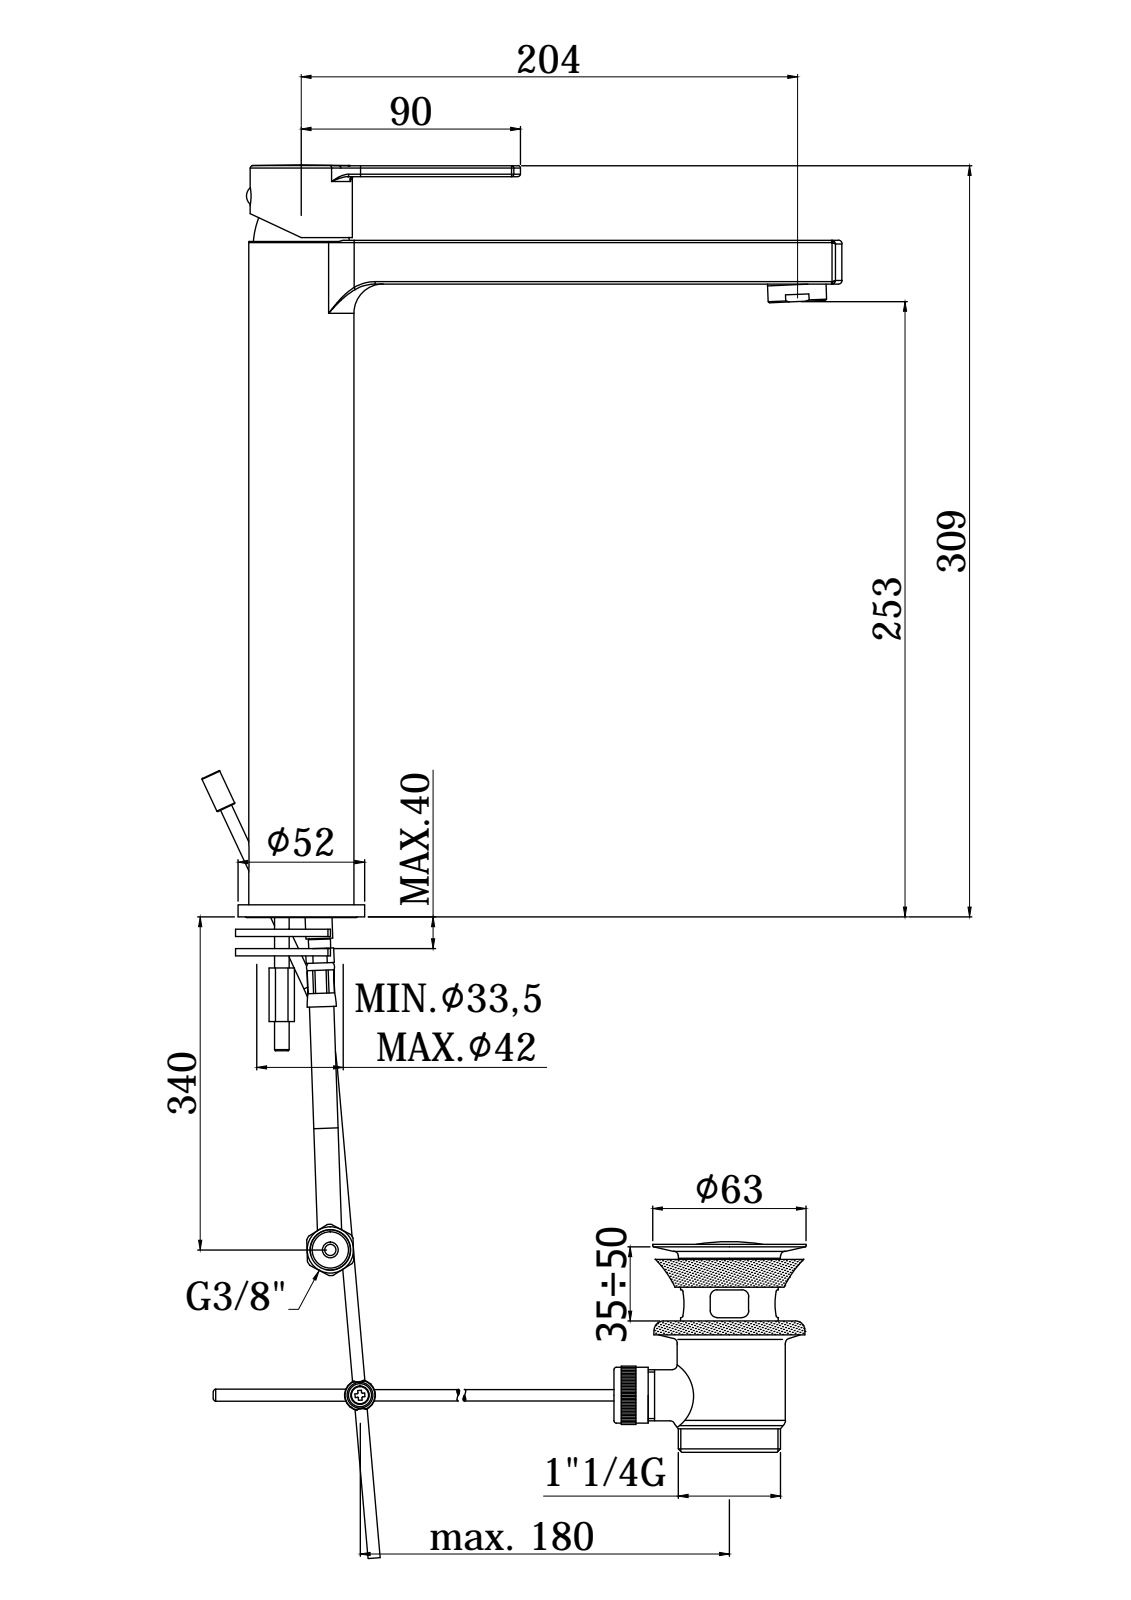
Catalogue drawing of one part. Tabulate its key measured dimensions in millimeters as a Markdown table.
| quantity | value |
| --- | --- |
| part name | RIN085CR |
| STEP written by | CREO PARAMETRIC BY PTC INC, 2020044 (CONFIG_CONTROL_DESIGN) |
| units | millimeters |
| bodies | 7 solids, 3005 faces (2168 planar, 415 cylindrical, 422 other) |
| overall size | 310.92 × 263.5 × 52 |
| volume | 247 687 mm³ |
| surface area | 164 539 mm² |
| round holes (diameter × count) | 6 × 4, 8.2 × 4, 4 × 3, 5 × 3, 5.5 × 2, 6.5 × 2, 7 × 2, 8 × 2, 3 × 1, 3.3 × 1, 7.8 × 1, 16 × 1 |
| round bosses / shafts (diameter × count) | 8 × 5, 19.5 × 2, 11 × 2, 6 × 2, 4.8 × 2, 4 × 2, 52 × 1, 43.2 × 1 |
| partial cylindrical surfaces (radius × count) | 1 × 29, 0.5 × 22, 1.5 × 20, 2 × 9, 1.7 × 6, 0.8 × 4, 5.8 × 4, 20 × 4 |
| main face-to-face distances | 3.5, 14.5, 18, 11, 27.5, 31, 1, 24, 7.5, 45.55 |
| hole center spacings | 14, 13.6, 2.83, 8.6, 13.45, 15.13, 20.1, 21.93 |
